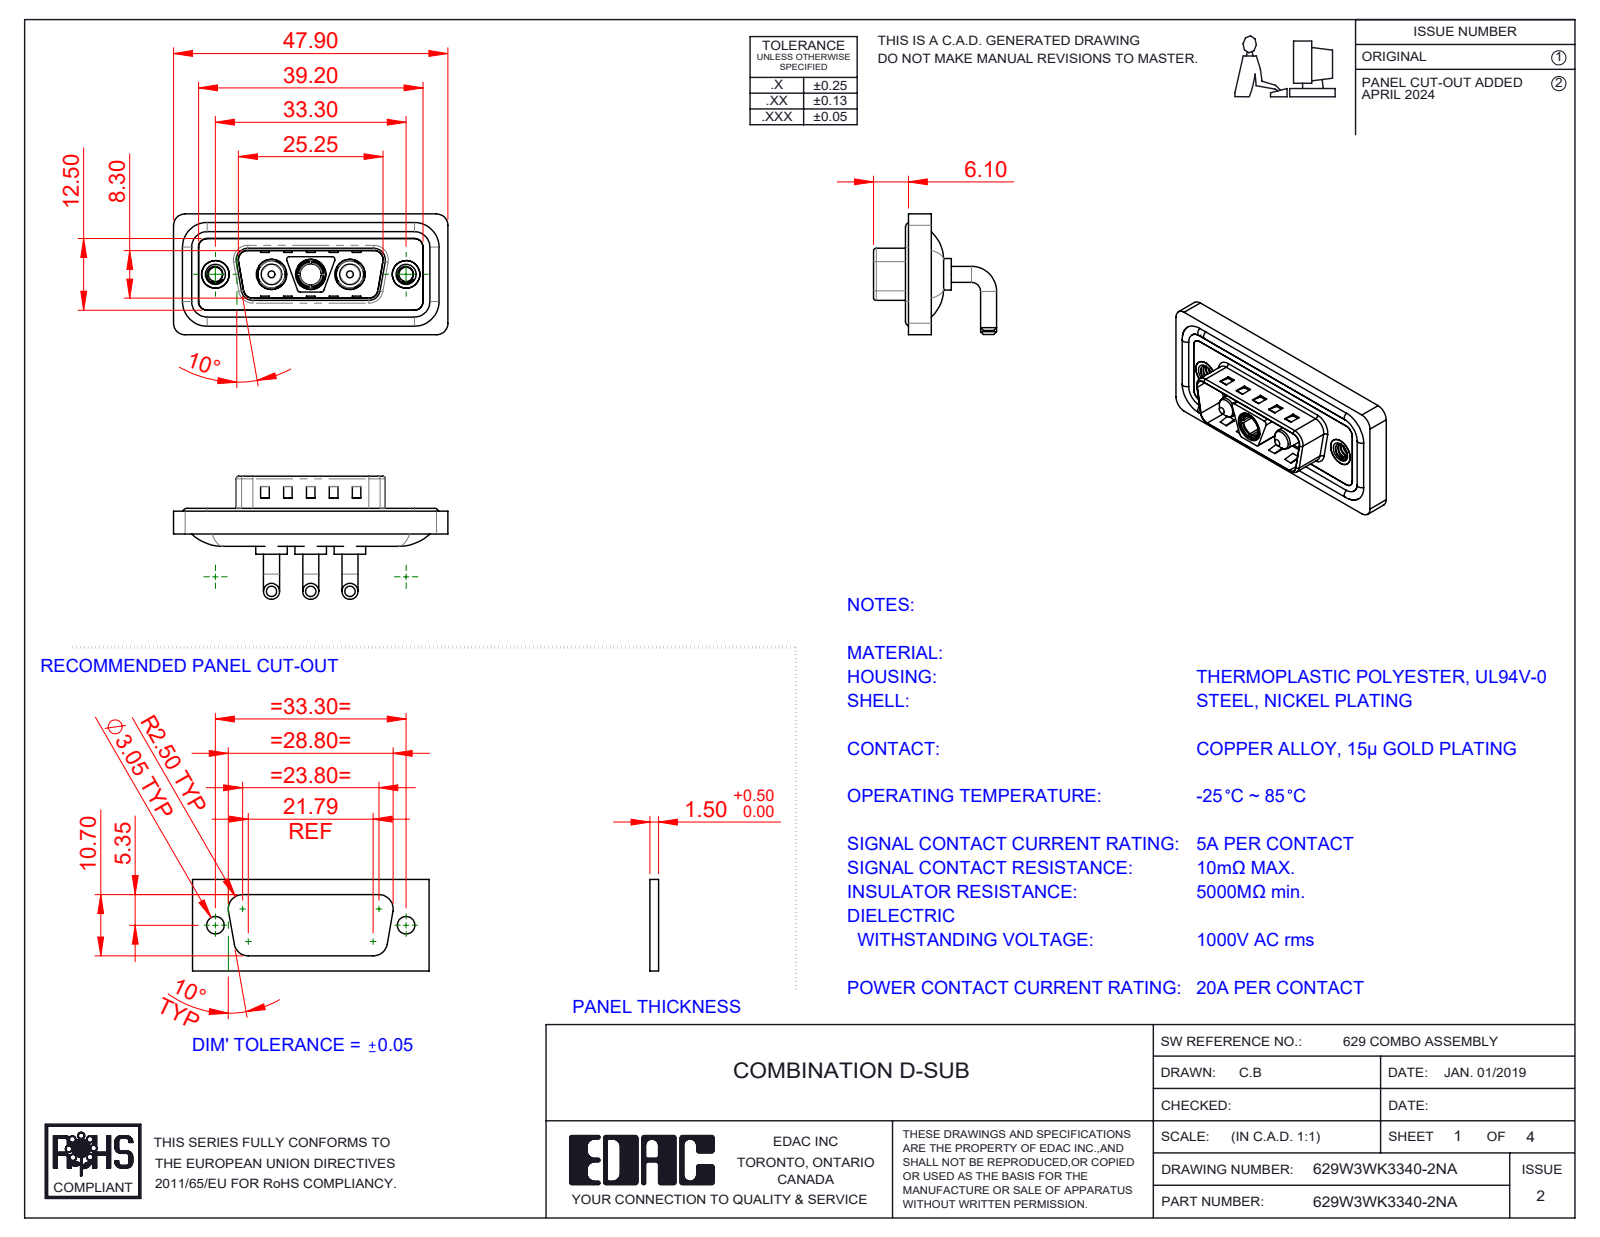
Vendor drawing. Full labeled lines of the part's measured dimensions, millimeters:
Part name (STEP PRODUCT): Power Pin_20A RA; 629Combo Threaded Rivet_A; 629W3WK3340-2NA; Power Socket_20A RA (+4 more)
STEP written by: SolidWorks 2023 (CONFIG_CONTROL_DESIGN)
Units: millimetres
Bodies: 13 solids, 615 faces (231 planar, 254 cylindrical, 130 other)
Overall size (bounding box): 47.9 × 21.5 × 21.1
Volume: 5 888 mm³ · Surface area: 9 419 mm²
Round holes (diameter × count): ⌀4.85 ×3, ⌀5.3 ×3, ⌀2.5 ×2, ⌀4 ×2, ⌀4.8 ×2, ⌀5 ×2, ⌀3.7 ×1
Round bosses / shafts (diameter × count): ⌀2.8 ×6, ⌀1.6 ×4, ⌀5.5 ×3, ⌀5.2 ×3, ⌀4.75 ×3, ⌀3.75 ×3, ⌀4.9 ×2, ⌀3.6 ×2
Partial cylindrical surfaces — rounded edges, fillets, slot ends (radius × count): R2 ×20, R1.5 ×18, R0.5 ×12, R1.6 ×8, R0.25 ×4, R0.6 ×4, R0.65 ×4, R0.9 ×4
Main face-to-face distances: 0.4, 2.9, 0.8, 1.1, 2.1, 1.6, 4.5, 3.1, 2.5, 3.7
Hole centre spacings: 6.85, 9.8, 16.65, 23.5, 13.7, 33.3
